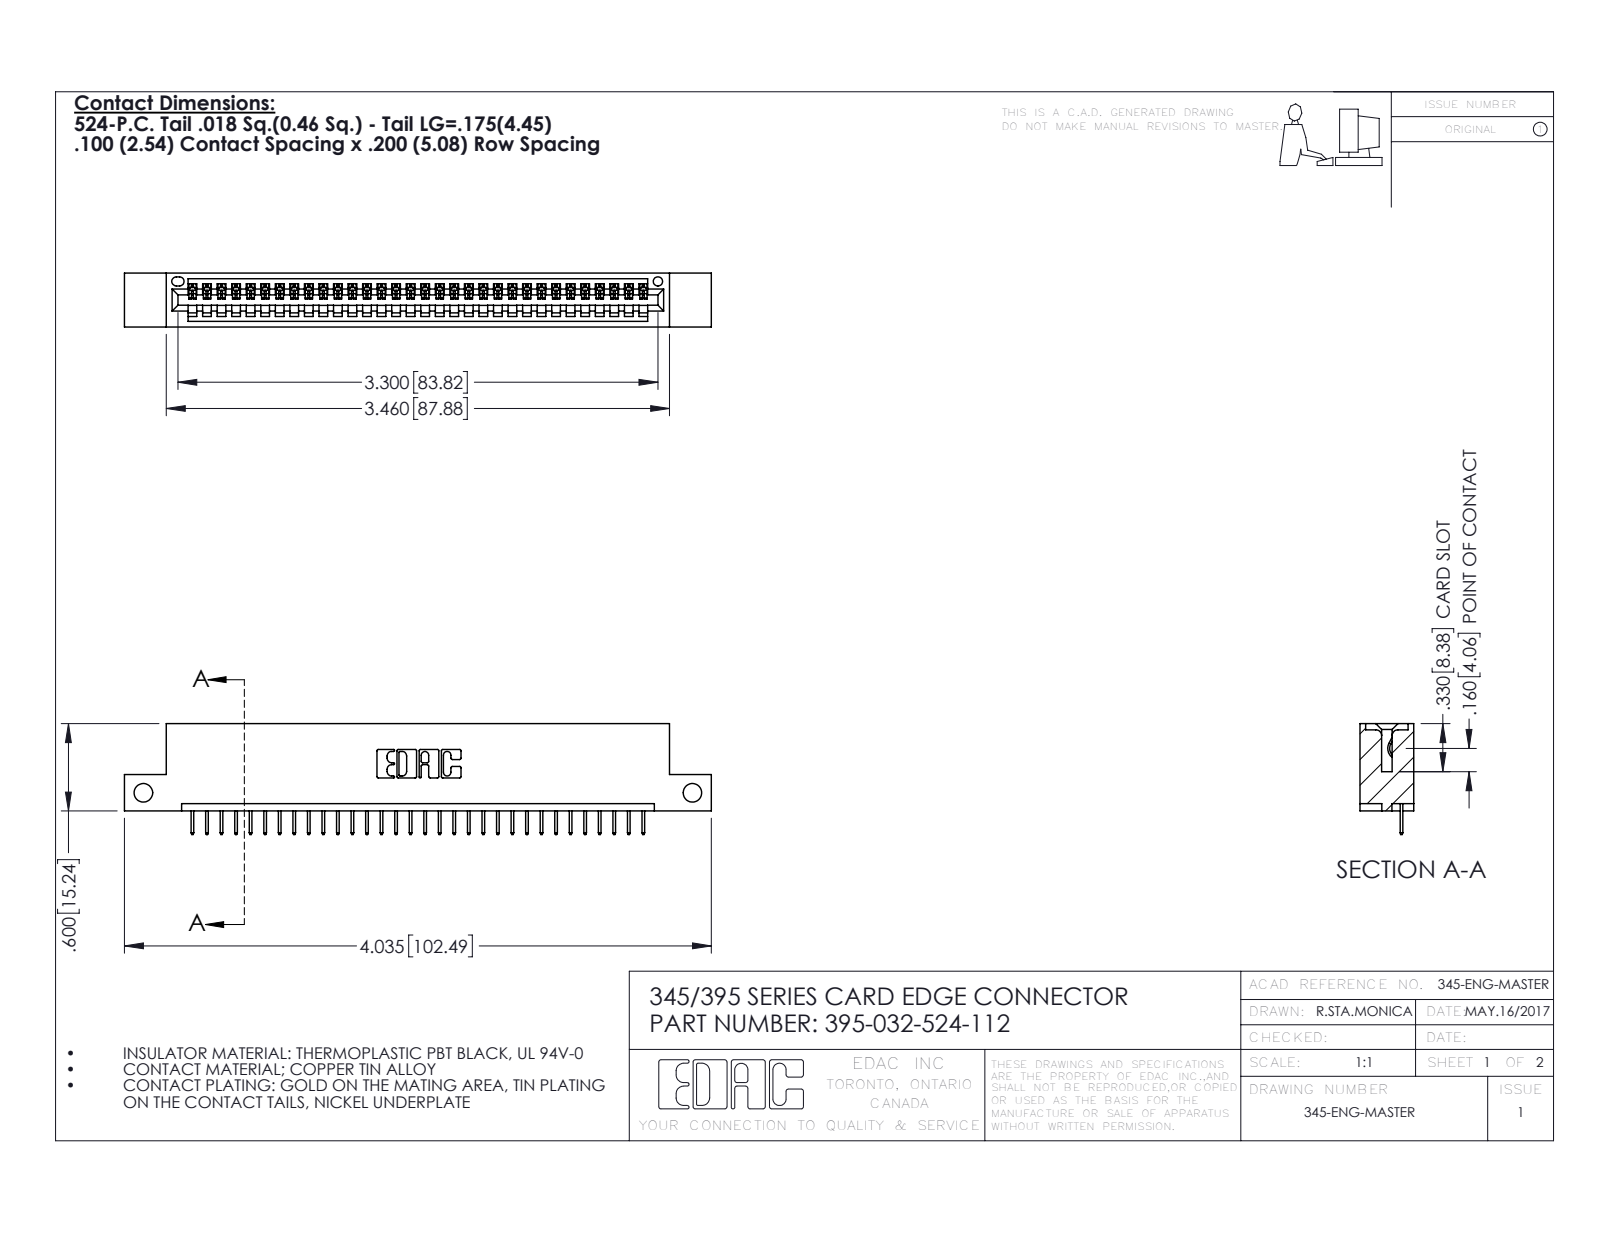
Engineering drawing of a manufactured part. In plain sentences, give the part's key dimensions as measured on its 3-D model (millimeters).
The part is named "345-292-001_345-293-124; 395-032-524-112; 345 Part_Flush Mounting Lugs - Side Mount". Its 3-D file was written by "SolidWorks 2016 (CONFIG_CONTROL_DESIGN)". It is 33 solids with 2110 faces: 1552 planar, 558 cylindrical and 0 other. Overall it measures 102.5 by 19.4 by 9.4 millimeters. Its volume is 9 440 cubic millimeters and its surface area 11 860 square millimeters. Round holes: 2 of diameter 3.3, 1 of diameter 1.6. Partial cylindrical surfaces (rounded edges, fillets, slot ends): 64 of radius 0.2, 22 of radius 0.3, 6 of radius 0.2, 6 of radius 0.8, 3 of radius 0.7, 2 of radius 0.8, 2 of radius 1, 1 of radius 0.4. The main face-to-face distances are 1.8, 7.6, 9.4, 5.1, 2.5, 6.9, 0.6, 5.7, 1.8, 3.8. The hole center spacings are 95.9.
